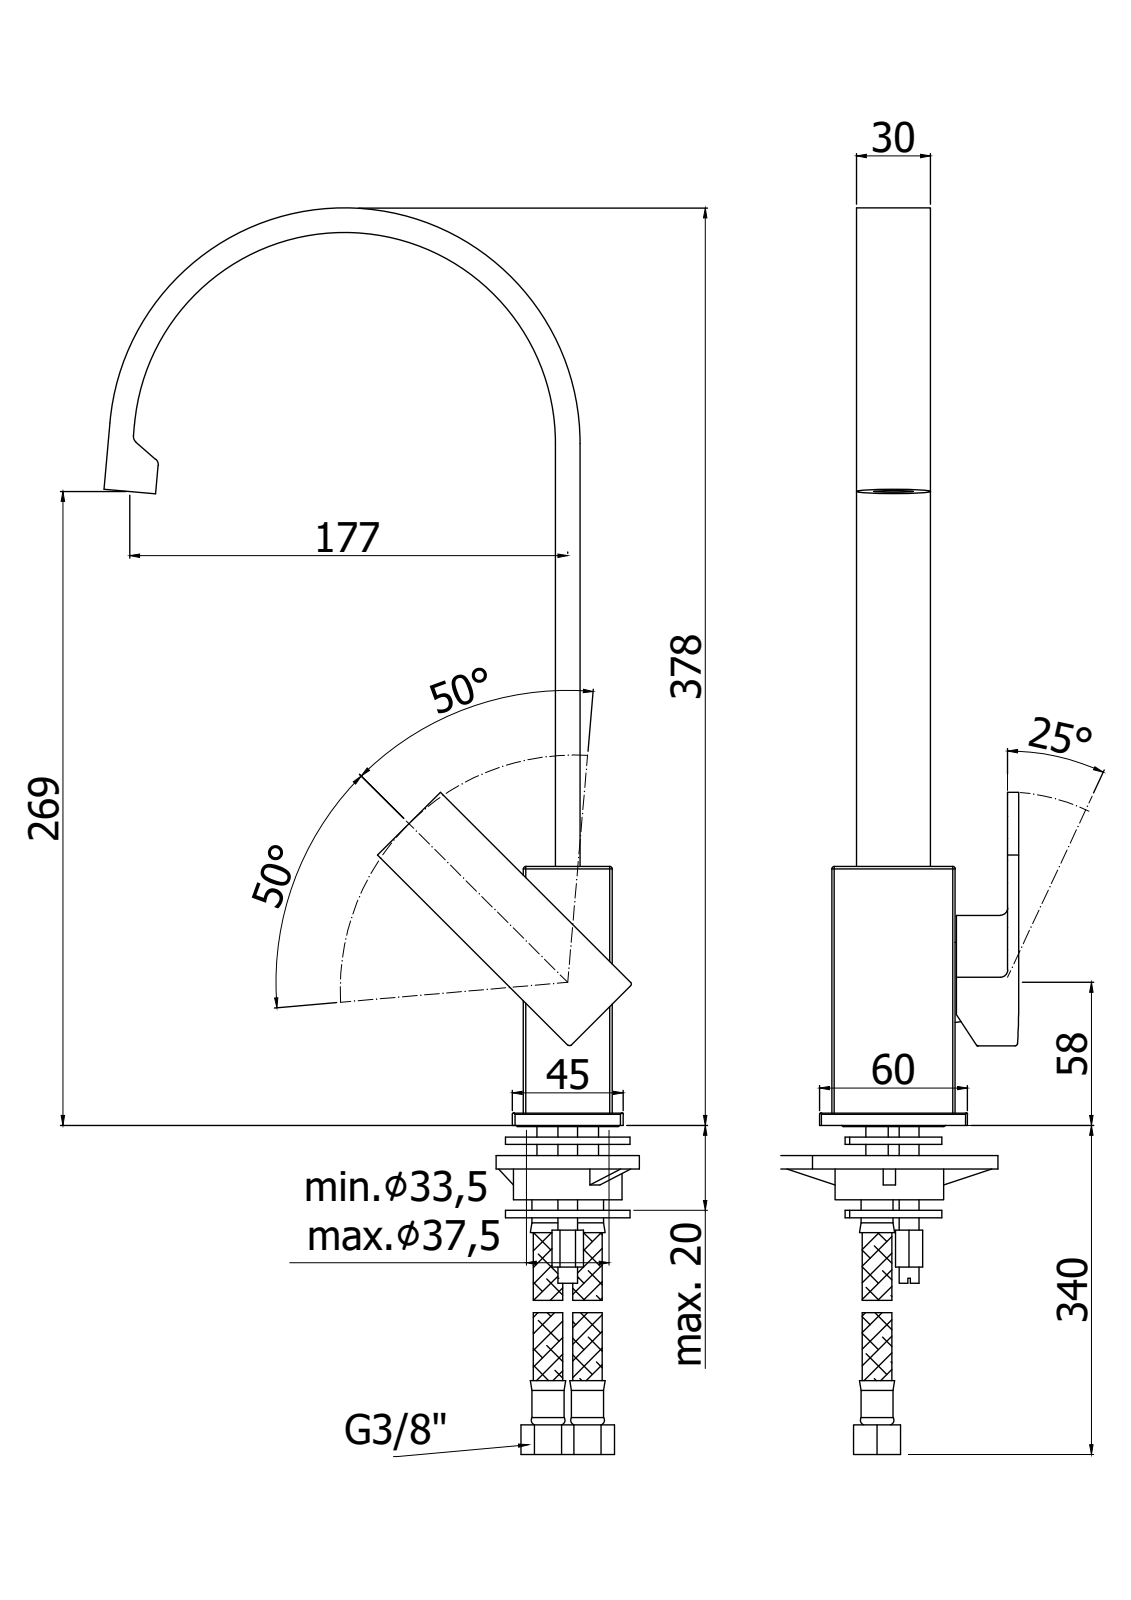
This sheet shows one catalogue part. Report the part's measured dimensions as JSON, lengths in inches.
{"part_name": "EL880CR", "step_written_by": "CREO PARAMETRIC BY PTC INC, 2020044 (CONFIG_CONTROL_DESIGN)", "units": "inches", "bodies": {"solids": 2, "faces": 293, "planar": 88, "cylindrical": 119, "other": 86}, "overall_size": [14.882, 8.356, 3.279], "volume_in3": 19.86, "surface_area_in2": 139.2, "round_holes": [[0.236, 3], [0.118, 2], [0.126, 2], [0.197, 2], [0.217, 2], [0.354, 2], [0.433, 2], [0.157, 1], [0.177, 1], [0.268, 1], [0.315, 1], [0.63, 1]], "round_bosses_or_shafts": [[1.528, 1], [0.787, 1], [0.346, 1], [0.299, 1]], "partial_cylinders_radius": [[0.039, 21], [0.059, 8], [0.197, 1], [1.181, 1], [3.356, 1], [3.749, 1]], "face_to_face_distances": [0.394, 0.906, 0.512, 1.417, 1.575, 1.181, 2.688, 1.507, 3.082, 1.113], "hole_center_spacings": [0.265, 0.352, 0.368, 0.371, 0.445, 0.601, 0.609, 0.118]}
